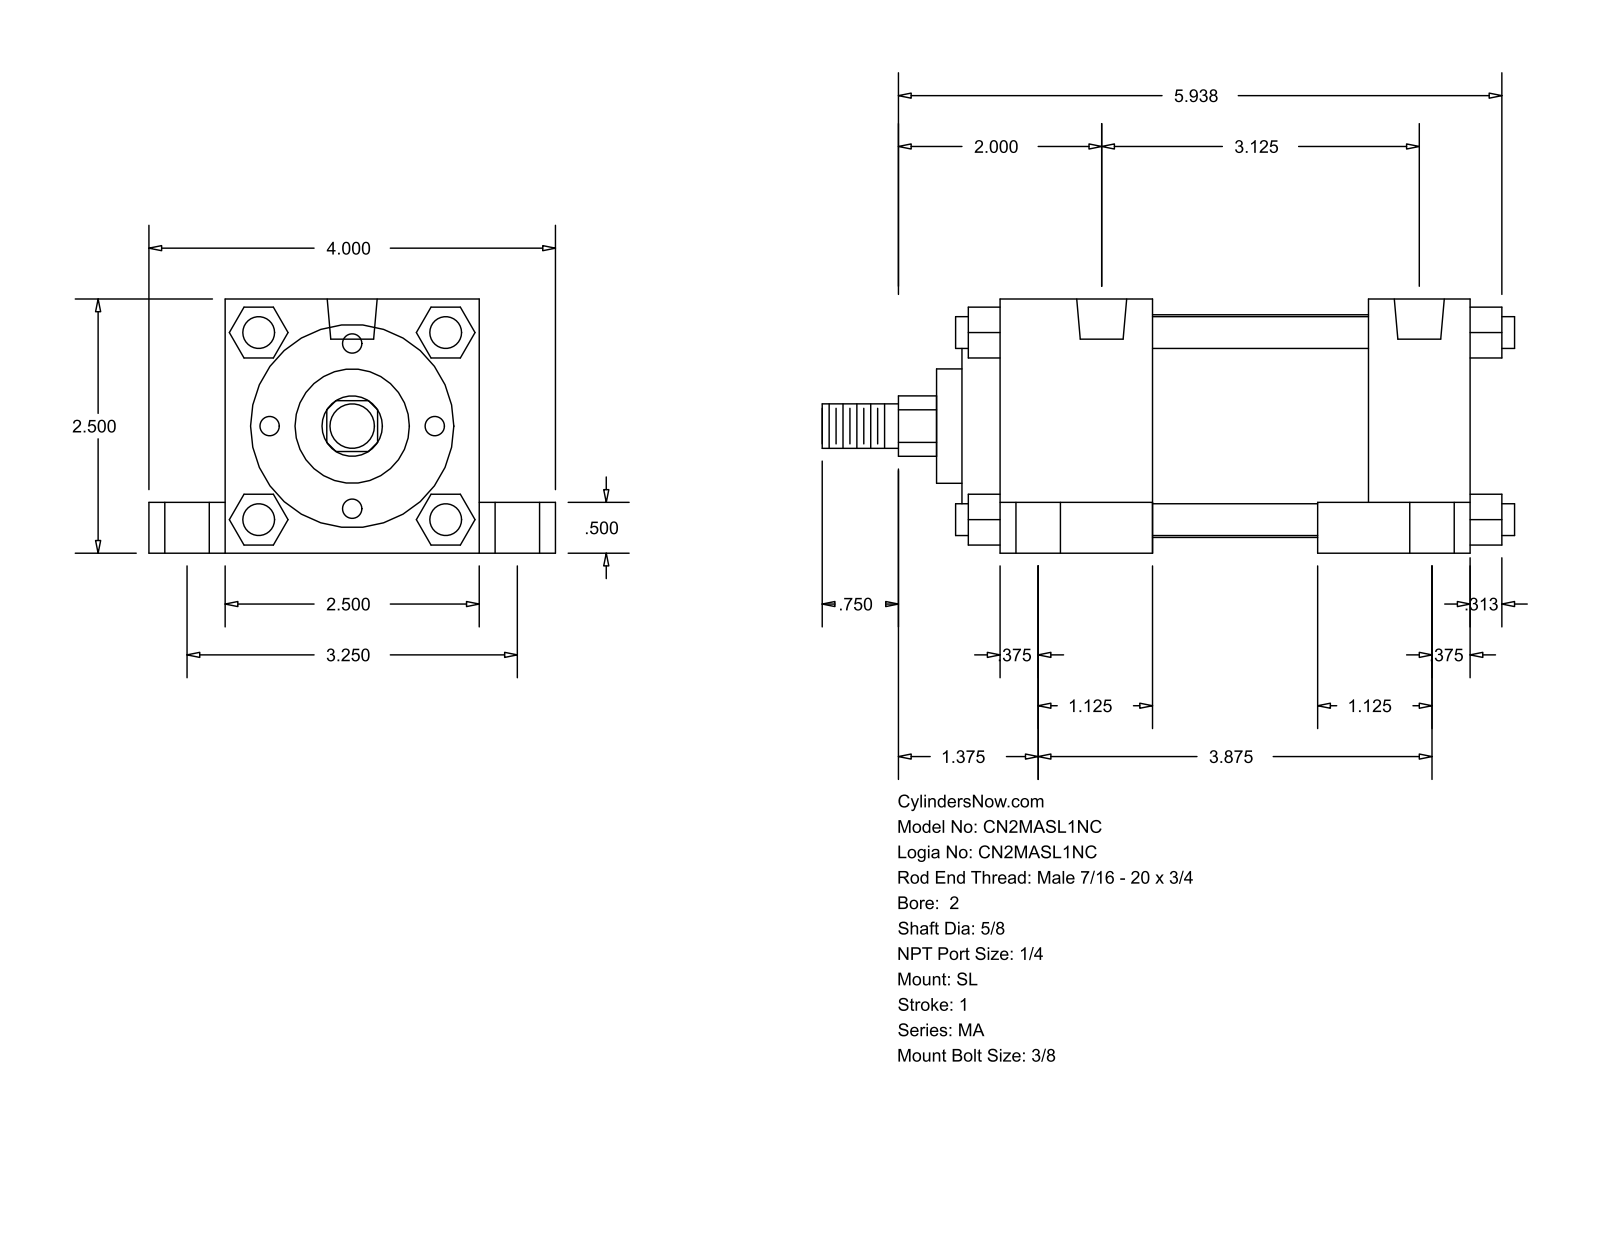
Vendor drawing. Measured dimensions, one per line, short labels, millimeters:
name: MA_SL__0200_0.625
written by: GSSL Pune (CONFIG_CONTROL_DESIGN)
unit: mm
bodies: 0 solids, 150 faces (113 planar, 37 cylindrical, 0 other)
size: 173.04 × 101.6 × 63.5
holes: 4× ⌀7.94, 4× ⌀11.11, 4× ⌀17.46, 2× ⌀12.49
bosses: 4× ⌀7.94, 1× ⌀55.63, 1× ⌀50.8, 1× ⌀28.57, 1× ⌀15.88, 1× ⌀11.11
rounds: 1× R7.54
face distances: 63.5, 12.7, 53.97, 9.52, 19.05, 82.55, 38.1, 50.8, 117.48, 79.38
hole spacings: 41.39, 44.22, 79.38, 82.54, 92.29, 98.43, 103.82, 128.46
